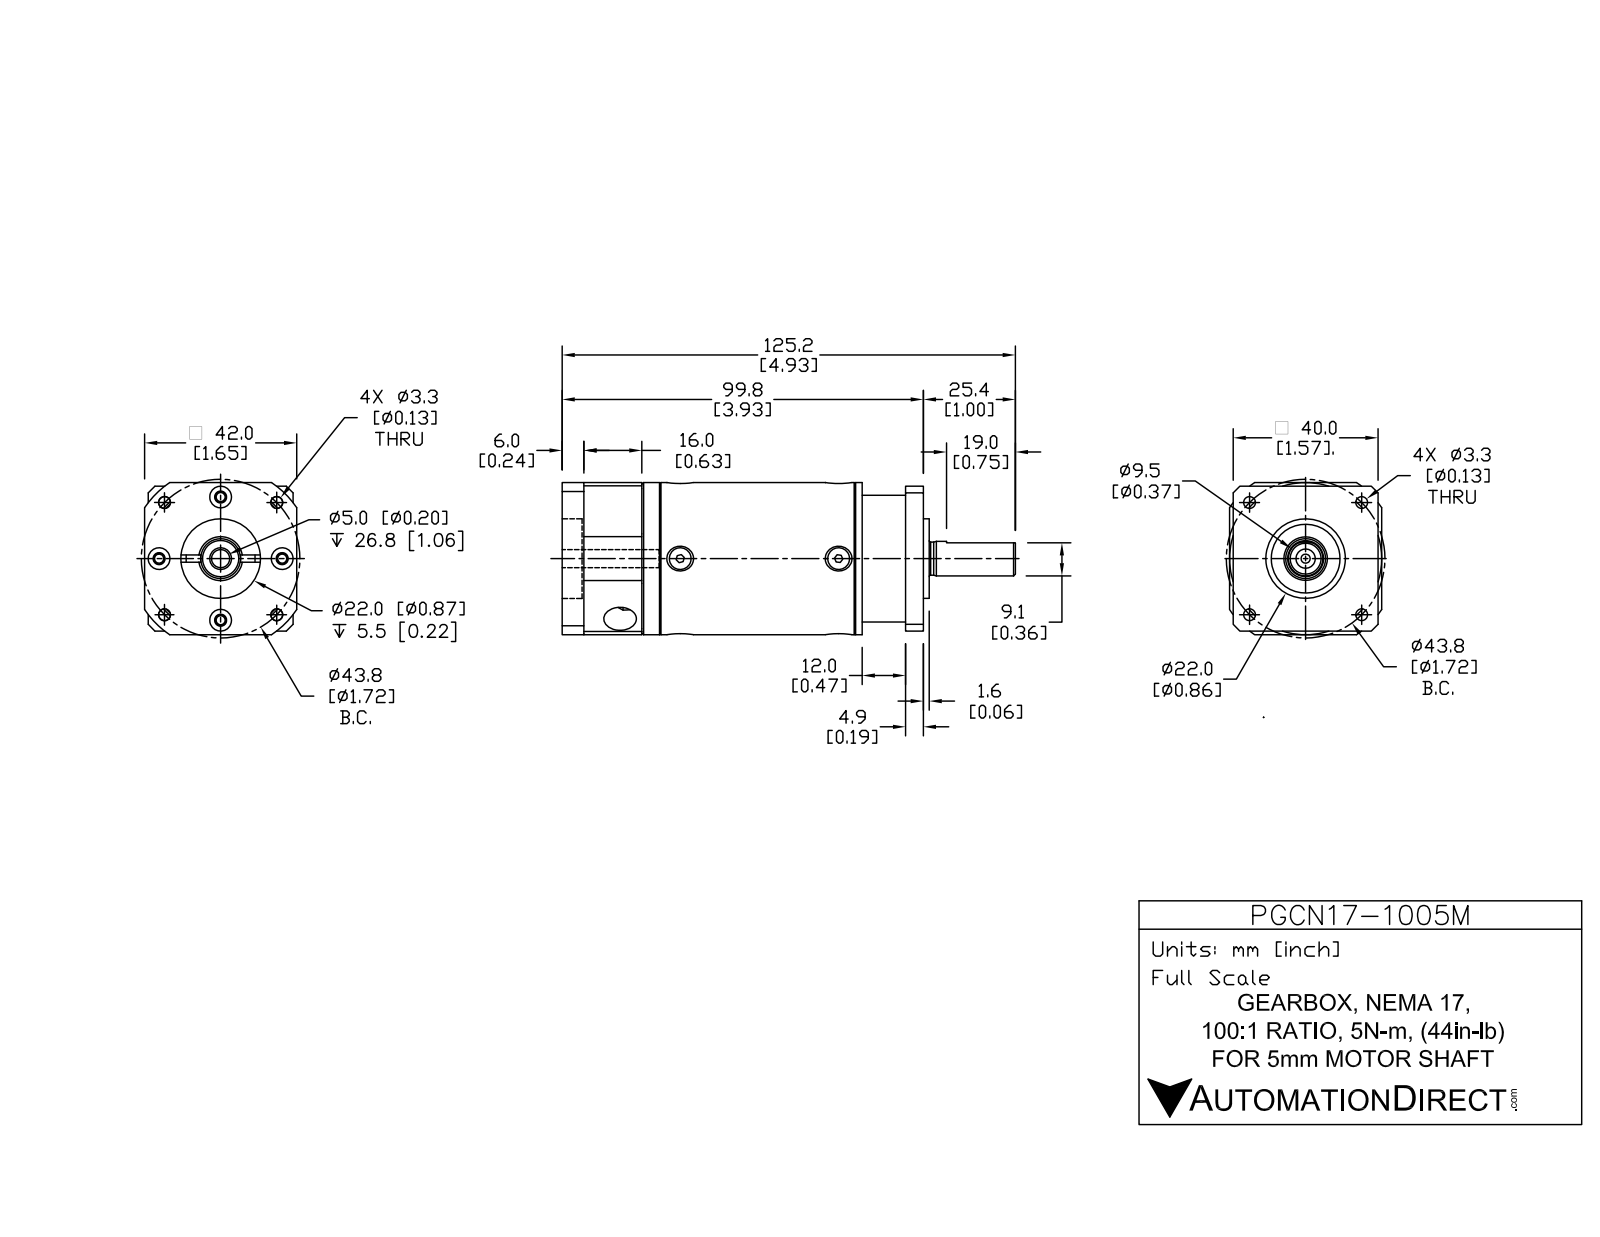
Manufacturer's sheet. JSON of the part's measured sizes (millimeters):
{"part_name": "Bushing_5x11x14.9_1; PE-N17-II 11mm Input; PGCN17-1005M; N17-E05_1", "step_written_by": "SolidWorks 2014 (AUTOMOTIVE_DESIGN)", "units": "millimeters", "bodies": {"solids": 3, "faces": 433, "planar": 137, "cylindrical": 174, "other": 122}, "overall_size": [125.1, 42, 42], "volume_mm3": 123800, "surface_area_mm2": 29270, "round_holes": [[3.3, 8], [2.5, 5], [3, 4], [3.3, 4], [3.4, 4], [6, 4], [4.5, 2], [9, 2], [5, 1], [11, 1], [19, 1], [22, 1]], "round_bosses_or_shafts": [[6, 4], [7, 2], [4, 2], [42, 1], [35, 1], [22, 1], [12, 1], [9.5, 1]], "partial_cylinders_radius": [[1.6, 2], [4, 2], [19, 1], [27, 1], [28, 1]], "face_to_face_distances": [22, 77.7, 99.7, 1, 41, 4.9, 72.8, 94.8, 37, 16], "hole_center_spacings": [15.6, 15.6, 31, 36, 36, 17, 21.9, 21.9]}
